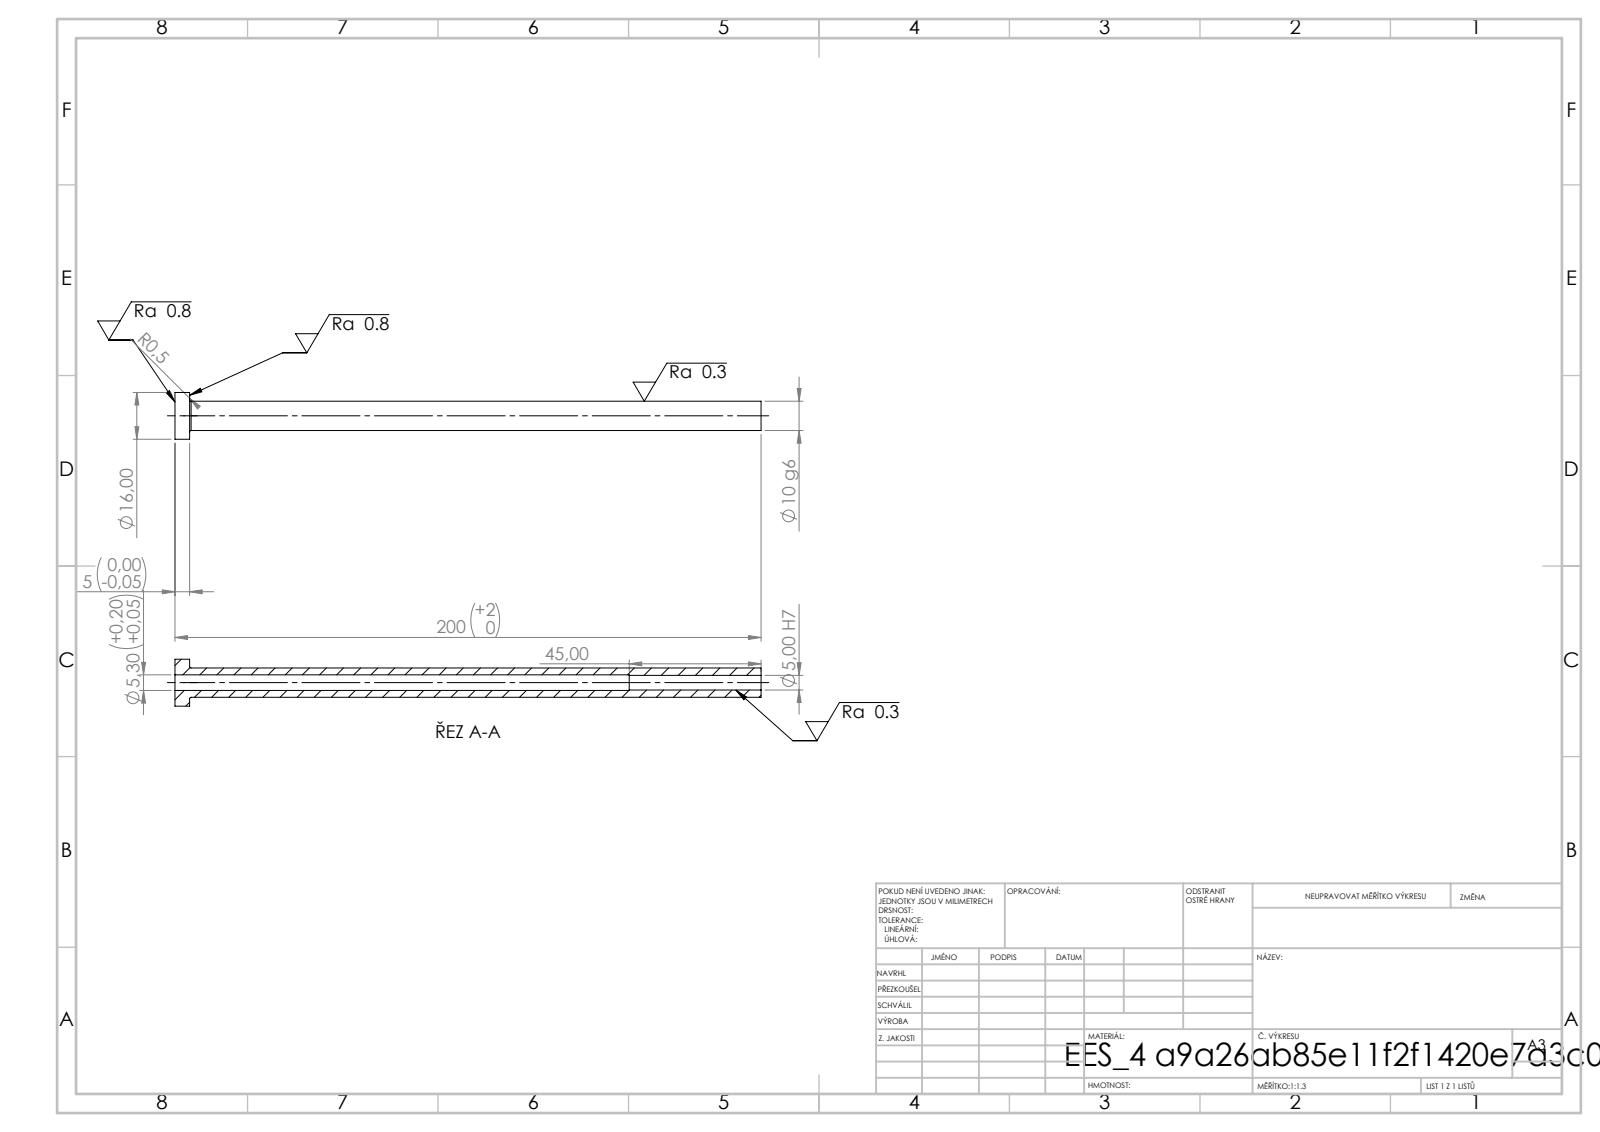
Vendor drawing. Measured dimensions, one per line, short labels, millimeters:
written by: SolidWorks 2019 (CONFIG_CONTROL_DESIGN)
unit: mm
bodies: 1 solid, 14 faces (4 planar, 8 cylindrical, 2 other)
size: 200 × 16 × 16
volume: 12 019 mm³; area: 10 021 mm²
holes: 1× ⌀5, 1× ⌀5.3
bosses: 1× ⌀16, 1× ⌀10
face distances: 5, 200, 195, 155, 150, 45
